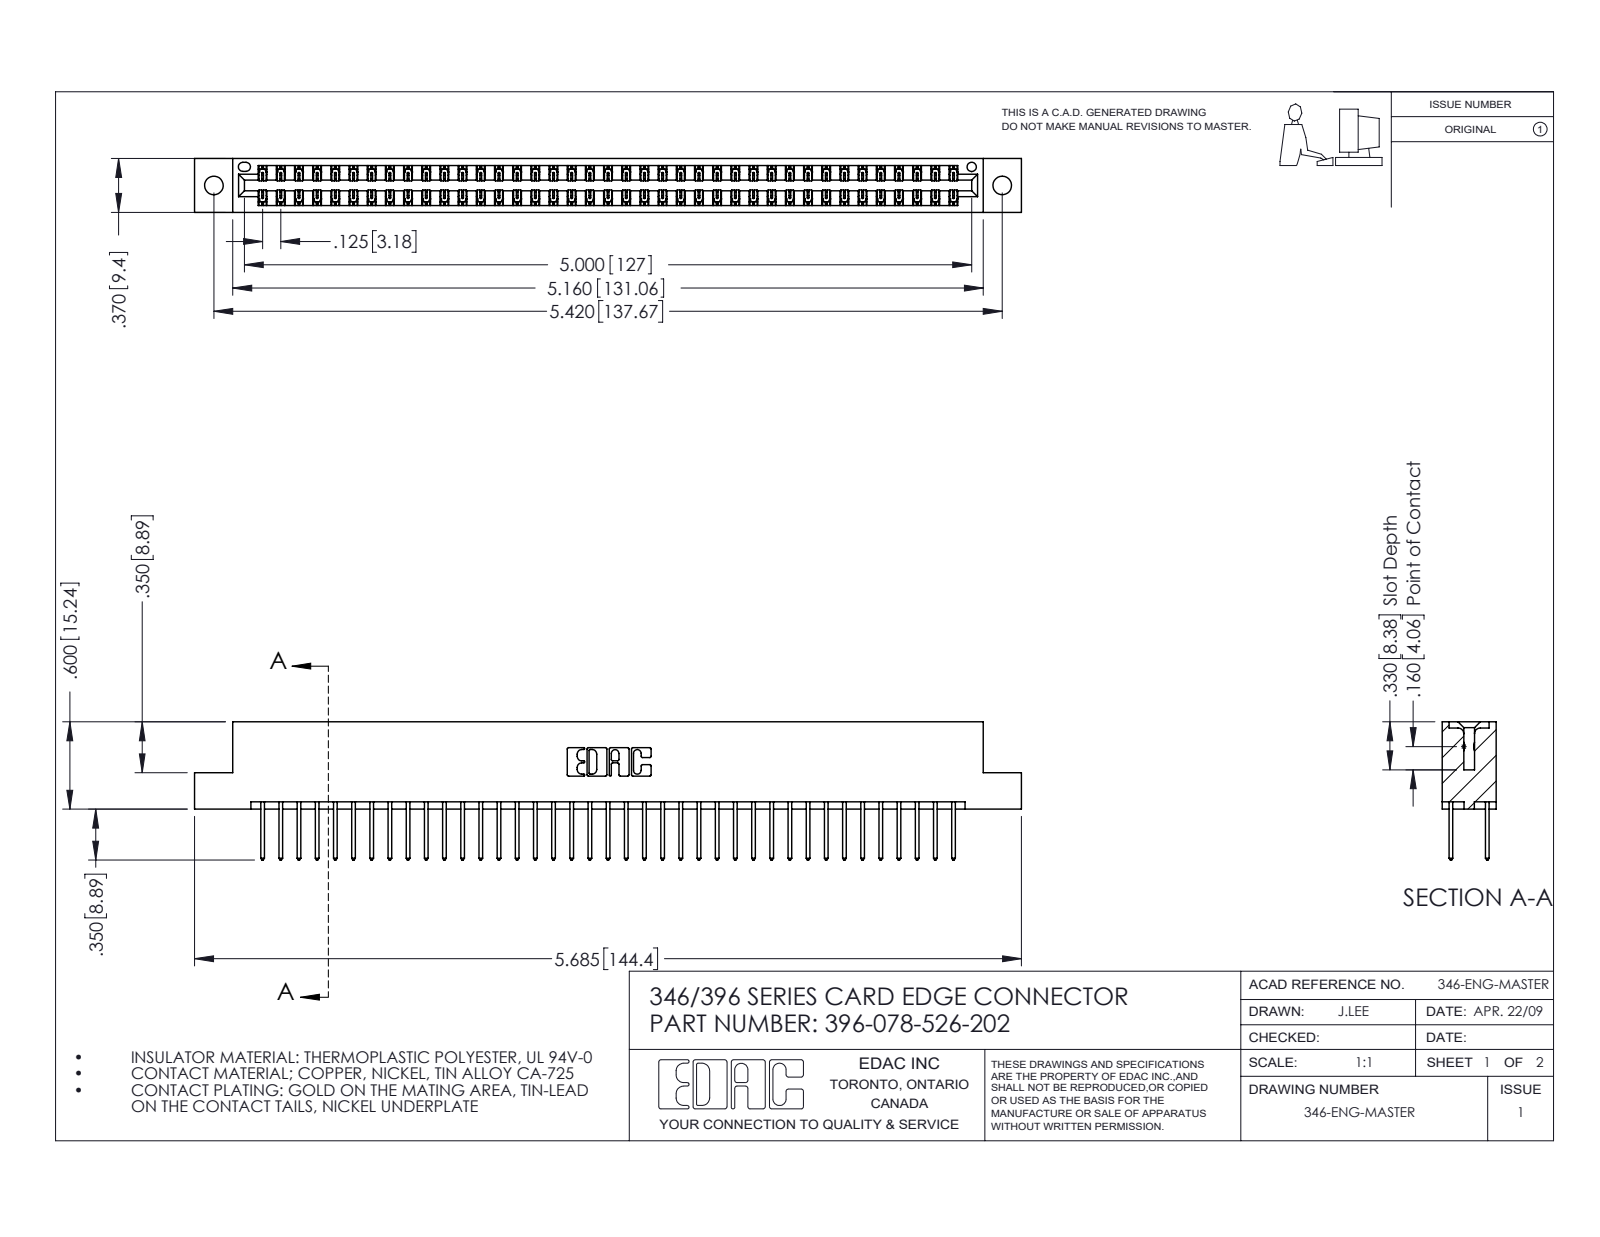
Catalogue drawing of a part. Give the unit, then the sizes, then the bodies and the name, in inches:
Units: inches
Overall size (bounding box): 5.685 × 0.95 × 0.37
Round holes (diameter × count): ⌀0.128 ×2, ⌀0.064 ×1
Partial cylindrical surfaces — rounded edges, fillets, slot ends (radius × count): R0.006 ×117, R0.01 ×78, R0.01 ×22, R0.007 ×6, R0.031 ×6, R0.026 ×3, R0.014 ×2, R0.022 ×2
Main face-to-face distances: 0.048, 0.322, 0.25, 0.37, 0.072, 0.298, 0.025, 0.275, 0.148, 0.222
Hole centre spacings: 0.246, 5.211, 5.42
Volume: 0.863 in³ · Surface area: 30.54 in²
Bodies: 79 solids, 4178 faces (2806 planar, 1372 cylindrical, 0 other)
Part name (STEP PRODUCT): 396-078-526-202; 346 Part_Flush Mounting Lugs - 0.128 Dia; 345-292-001_345-293-126
STEP written by: SolidWorks 2016 (CONFIG_CONTROL_DESIGN)
